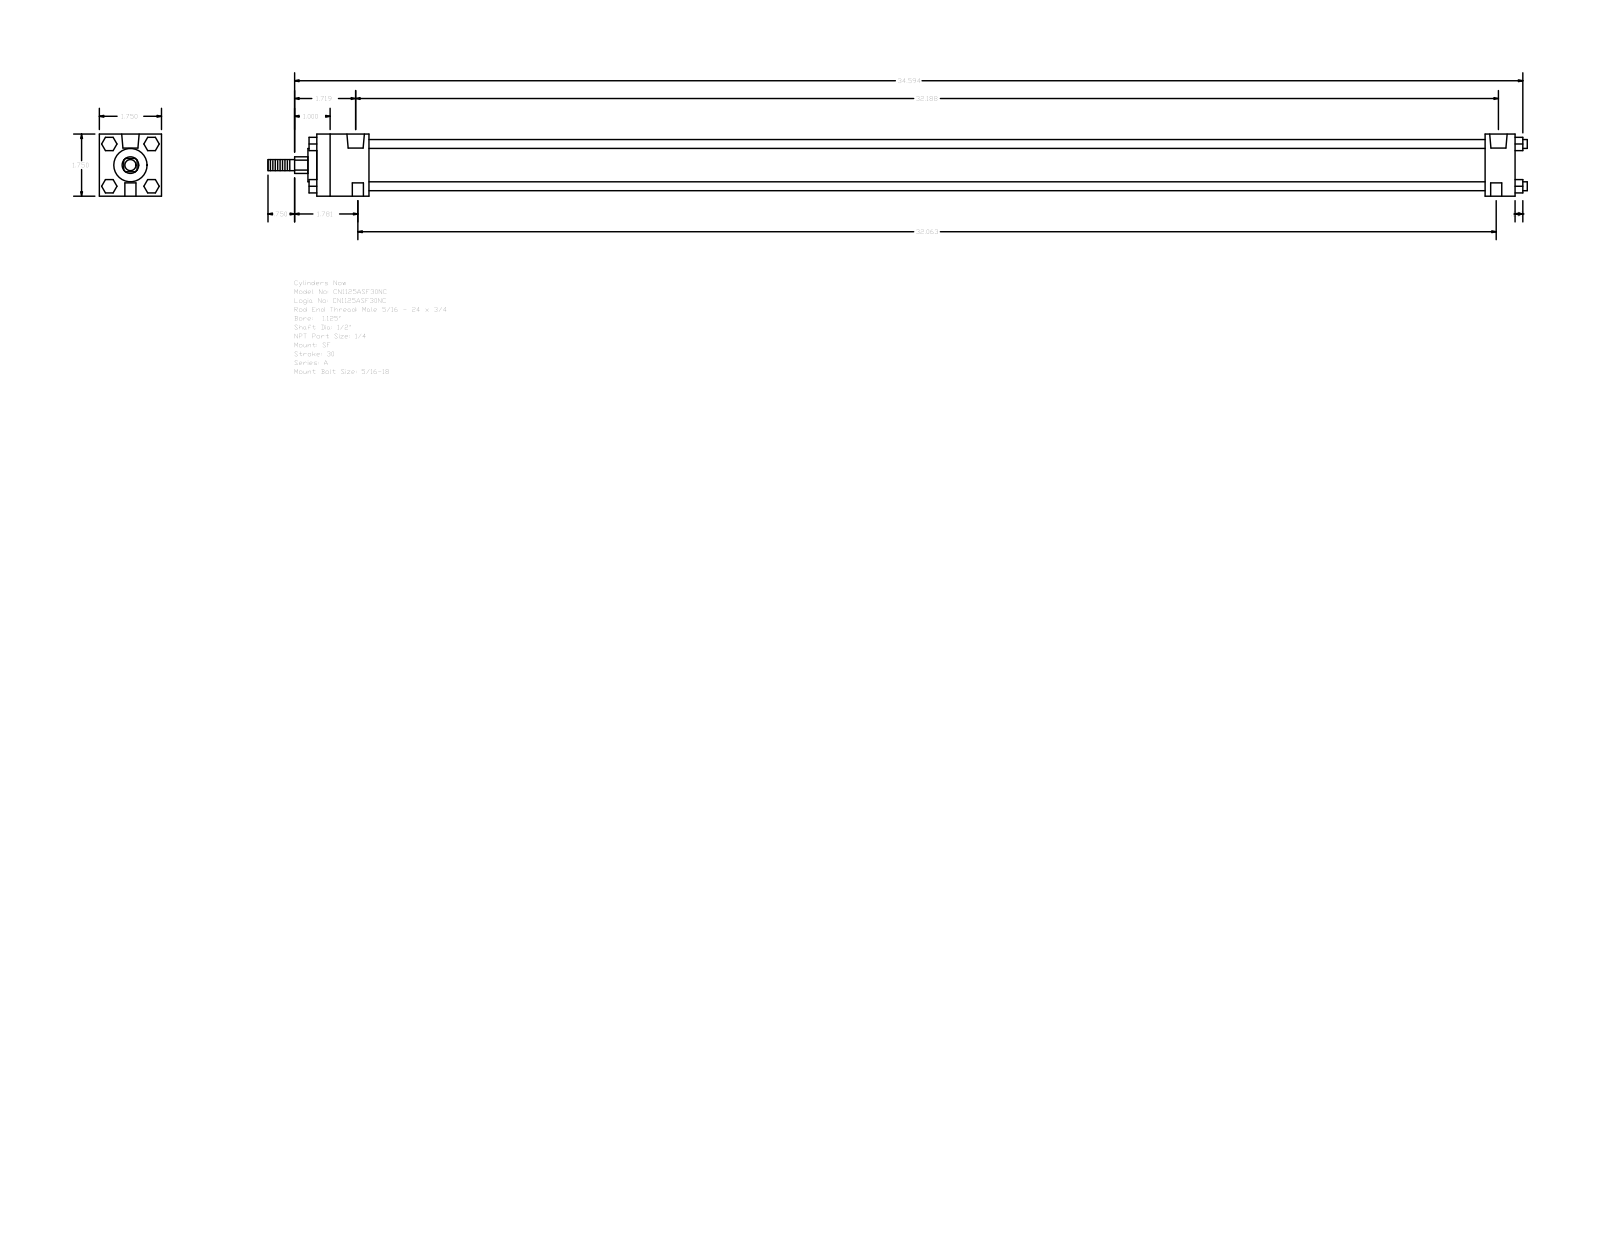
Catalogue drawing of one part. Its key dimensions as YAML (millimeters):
part_name: "A_SF__0112_0.5"
step_written_by: "GSSL Pune (CONFIG_CONTROL_DESIGN)"
units: millimeters
bodies: {solids: 0, faces: 120, planar: 92, cylindrical: 28, other: 0}
overall_size: [900.91, 44.45, 44.45]
round_holes:
  - {diameter: 5.56, count: 2}
  - {diameter: 7.94, count: 2}
  - {diameter: 12.49, count: 2}
round_bosses_or_shafts:
  - {diameter: 6.35, count: 4}
  - {diameter: 31.88, count: 1}
  - {diameter: 23.81, count: 1}
  - {diameter: 12.7, count: 1}
  - {diameter: 7.94, count: 1}
partial_cylinders:
  - {radius: 5.94, count: 1}
face_to_face_distances: [44.46, 857.24, 835.81, 21.43, 37.3, 798.51, 819.94, 9.53, 5.59, 5.56]
hole_center_spacings: [814.39, 1.58, 1.59, 815.97, 815.98, 817.56]
